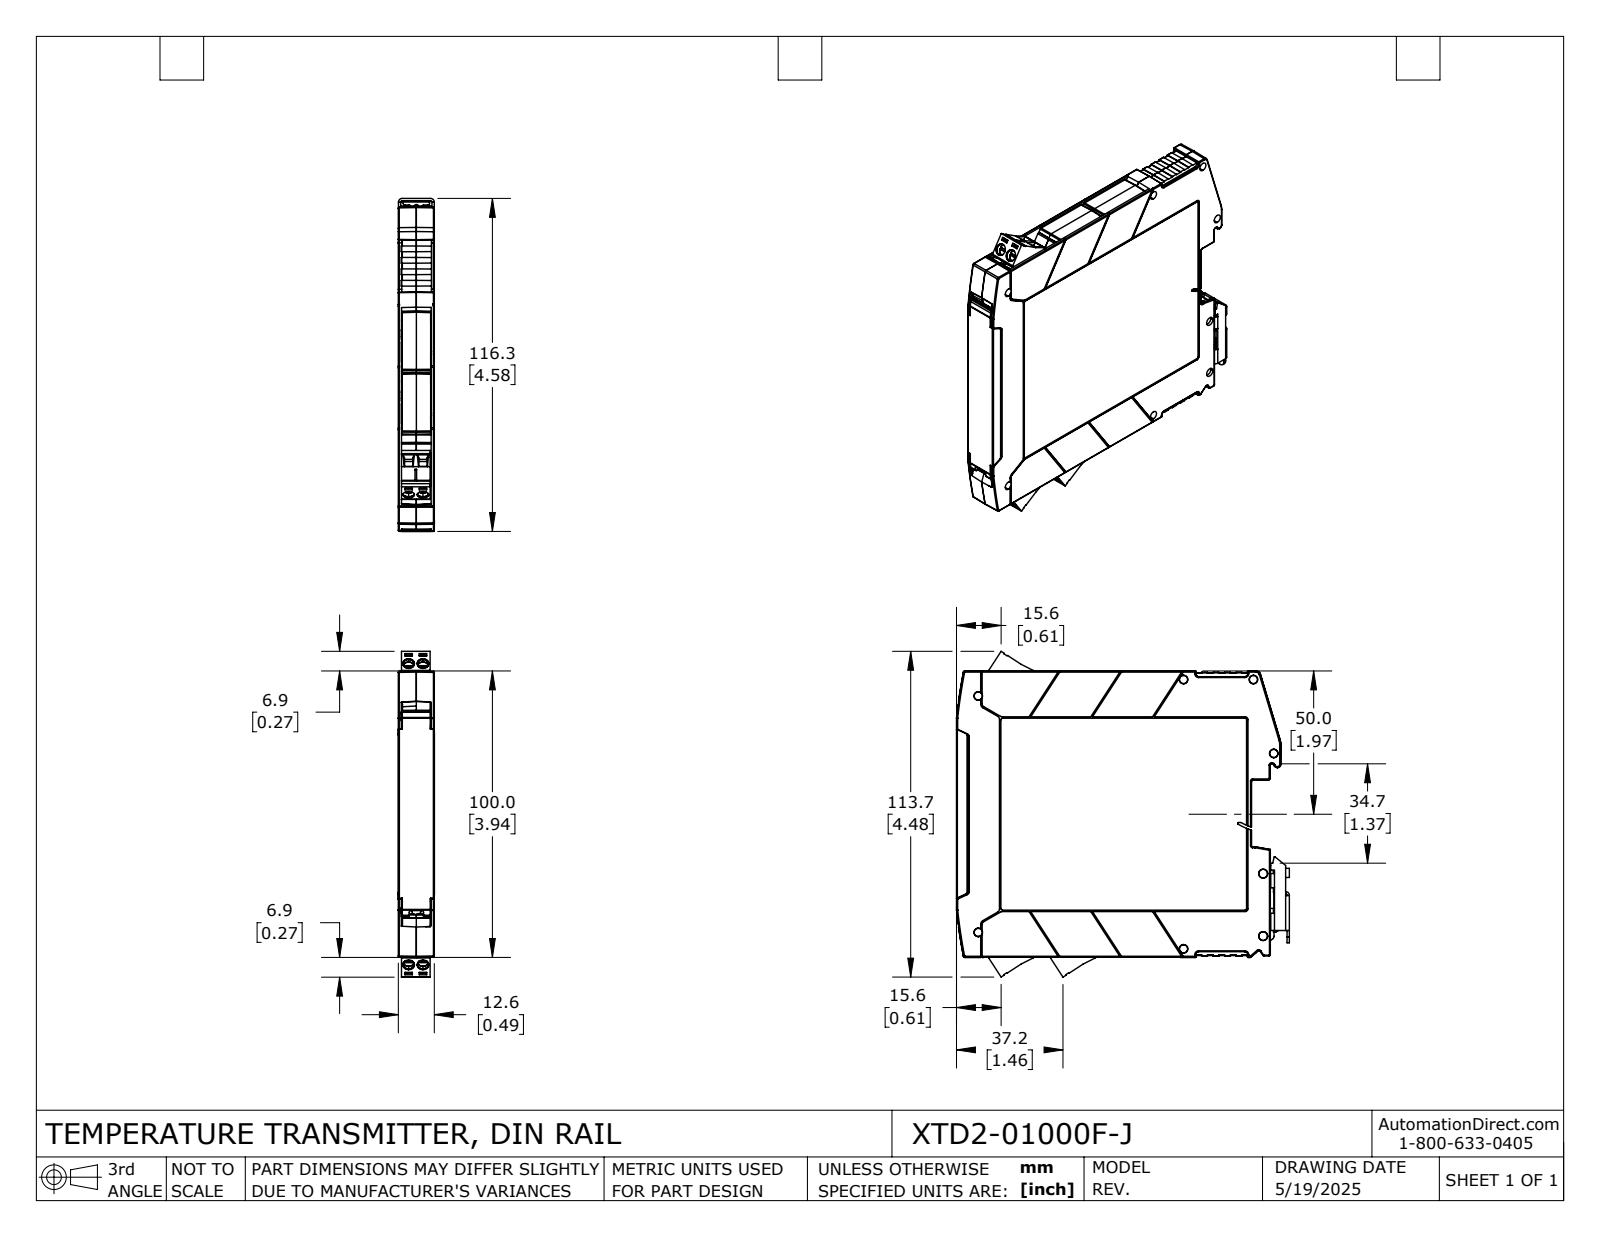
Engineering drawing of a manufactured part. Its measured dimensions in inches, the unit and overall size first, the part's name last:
Units: inches
Overall size (bounding box): 4.577 × 4.478 × 0.496
Round holes (diameter × count): ⌀0.063 ×6, ⌀0.11 ×6, ⌀0.152 ×6, ⌀0.159 ×6
Round bosses / shafts (diameter × count): ⌀0.156 ×6, ⌀0.098 ×6, ⌀0.059 ×2, ⌀0.053 ×2
Partial cylindrical surfaces — rounded edges, fillets, slot ends (radius × count): R0.008 ×89, R0.012 ×78, R0.02 ×71, R0.039 ×22, R0.004 ×20, R0.016 ×13, R0.006 ×12, R0.028 ×8
Main face-to-face distances: 0.049, 0.445, 0.494, 0.396, 0.043, 0.451, 0.402, 0.031, 0.198, 0.247
Hole centre spacings: 0.197, 0.464, 0.504, 0.713, 0.739
Volume: 2.41 in³ · Surface area: 101.5 in²
Bodies: 14 solids, 3337 faces (1910 planar, 596 cylindrical, 831 other)
Part name (STEP PRODUCT): XTD2-01000F-J
STEP written by: SolidWorks 2024 (AUTOMOTIVE_DESIGN)
